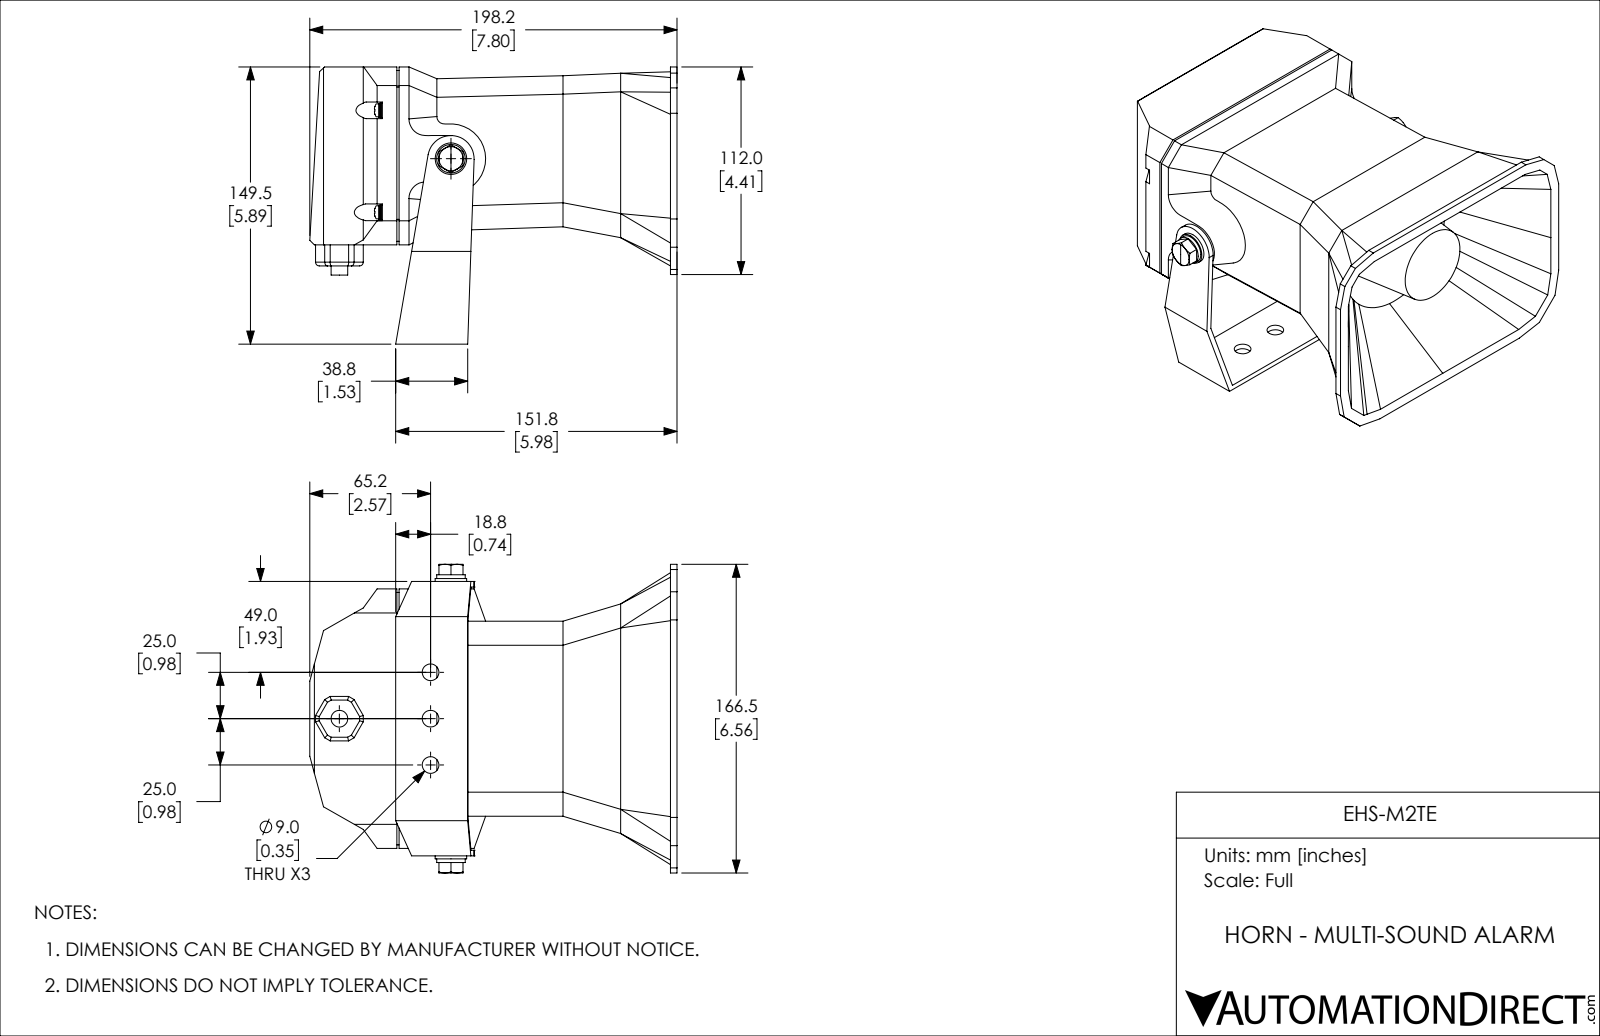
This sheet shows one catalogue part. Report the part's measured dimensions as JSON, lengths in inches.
{"part_name": "EHS-M2TE", "step_written_by": "SolidWorks 2018 (AUTOMOTIVE_DESIGN)", "units": "inches", "bodies": {"solids": 2, "faces": 306, "planar": 158, "cylindrical": 59, "other": 89}, "overall_size": [7.803, 6.557, 5.886], "volume_in3": 98.72, "surface_area_in2": 273, "round_holes": [[0.354, 3], [0.315, 1], [3.012, 1]], "round_bosses_or_shafts": [[0.315, 4], [0.299, 4], [0.669, 1], [0.606, 1], [0.354, 1]], "partial_cylinders_radius": [[0.079, 12], [0.492, 1]], "face_to_face_distances": [0.118, 3.78, 5.768, 2.106, 5.886, 1.988, 0.685, 4.827, 5.709, 4.143], "hole_center_spacings": [0.984, 1.969]}
